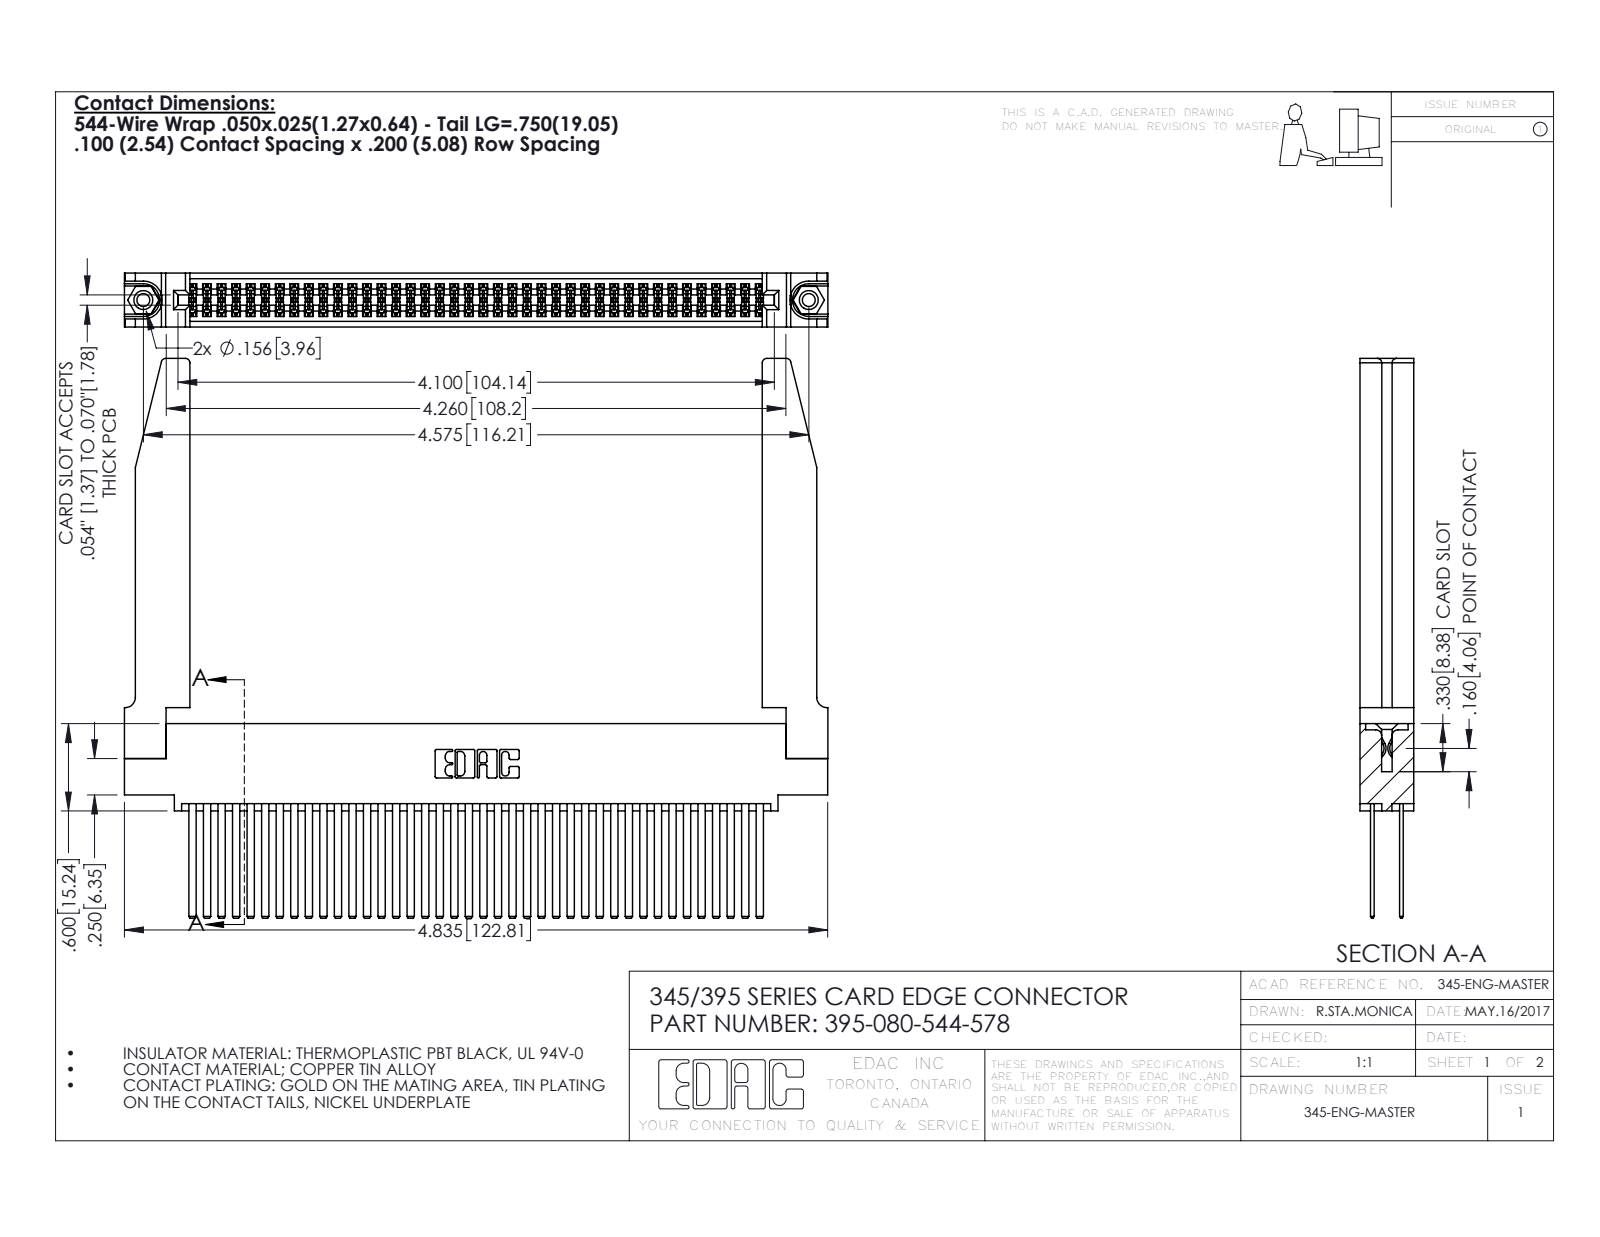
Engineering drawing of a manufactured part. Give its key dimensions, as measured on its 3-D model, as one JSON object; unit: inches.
{"part_name": "345 Part_0.110 Offset - 0.156 Dia-TH; 395-080-544-578; 345-292-001_345-293-144; 345-220-078_345-220-078 (+1 more)", "step_written_by": "SolidWorks 2016 (CONFIG_CONTROL_DESIGN)", "units": "inches", "bodies": {"solids": 85, "faces": 3884, "planar": 2546, "cylindrical": 1286, "other": 52}, "overall_size": [4.836, 3.847, 0.37], "volume_in3": 1.265, "surface_area_in2": 45.48, "round_holes": [[0.089, 2], [0.125, 2], [0.156, 2], [0.064, 1]], "round_bosses_or_shafts": [[0.155, 2]], "partial_cylinders_radius": [[0.006, 120], [0.01, 22], [0.03, 8], [0.007, 6], [0.031, 6], [0.026, 3], [0.014, 2], [0.019, 2]], "face_to_face_distances": [0.072, 0.298, 0.098, 0.272, 0.025, 0.2, 0.37, 0.225, 0.175, 0.148], "hole_center_spacings": [0.27, 4.339, 4.575]}
